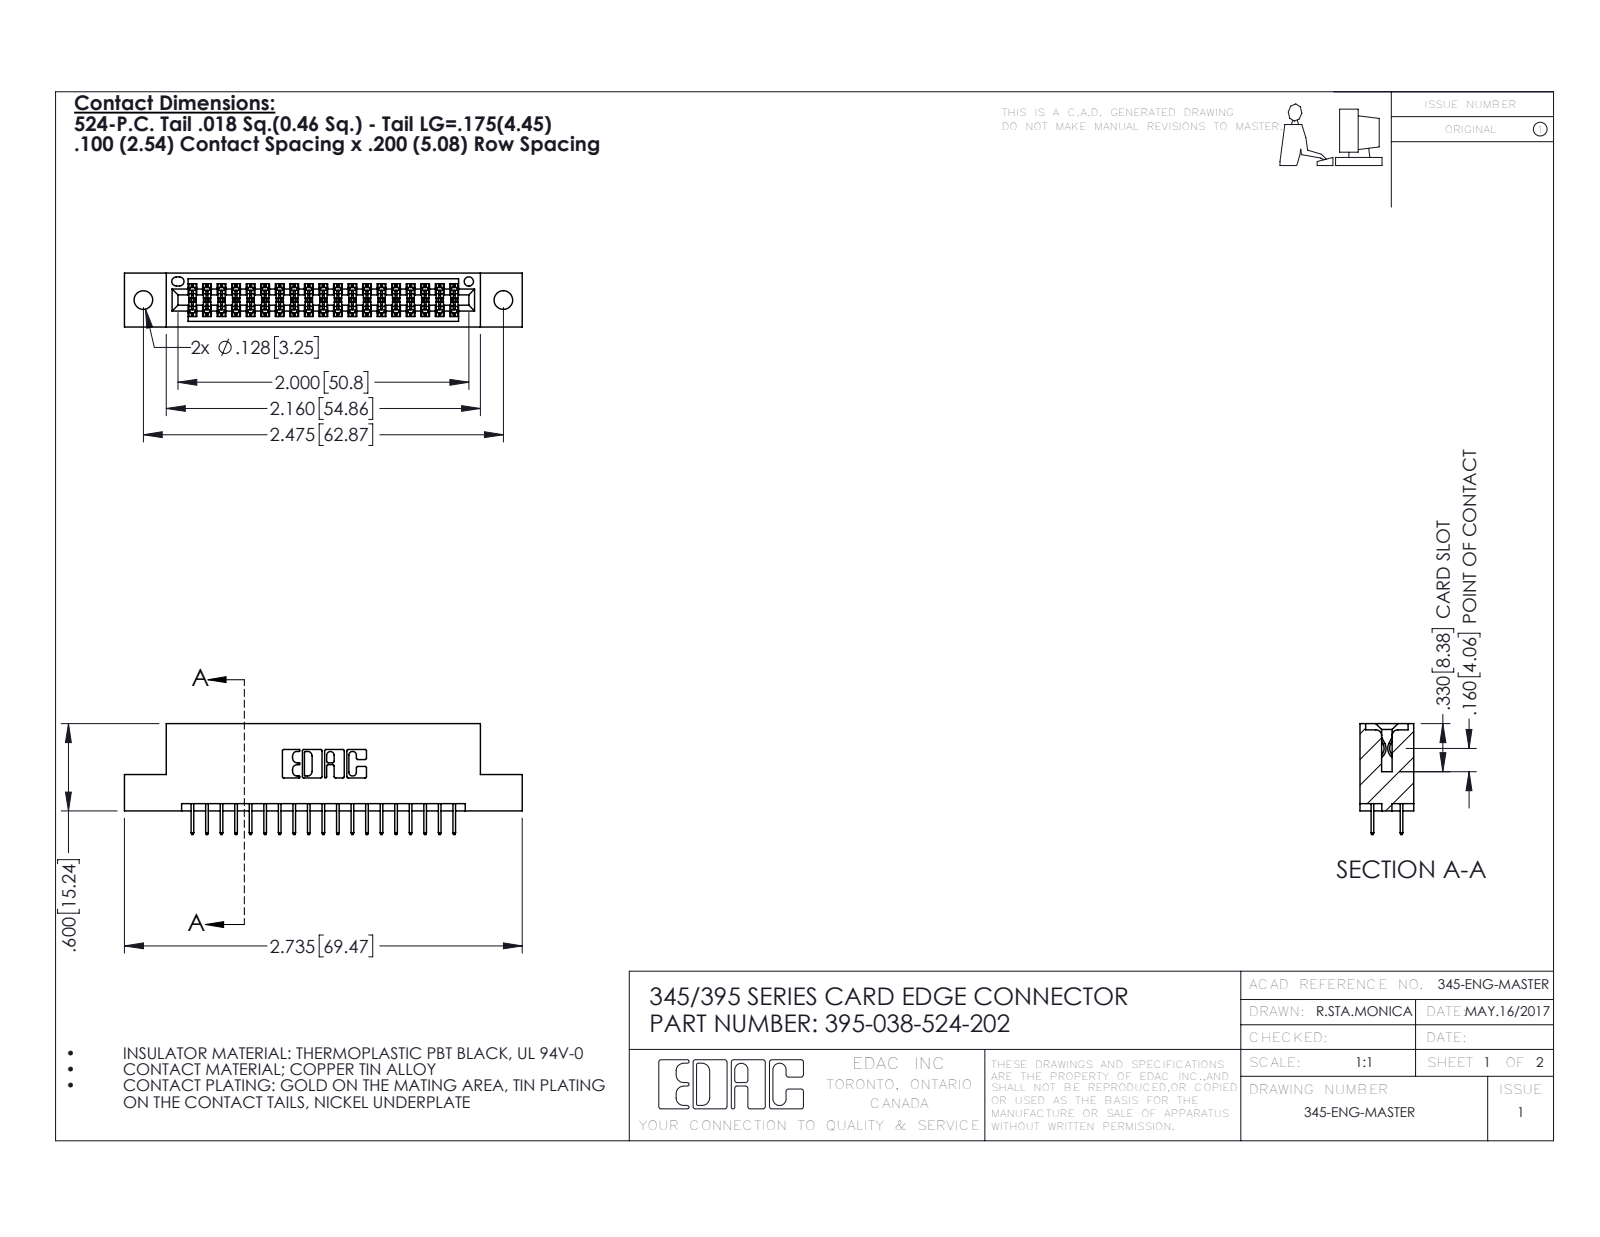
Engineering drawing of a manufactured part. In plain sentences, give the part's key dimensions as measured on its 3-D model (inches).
The part is named "345-292-001_345-293-124; 345 Part_Flush Mounting Lugs - 0.128 Dia; 395-038-524-202". Its 3-D file was written by "SolidWorks 2016 (CONFIG_CONTROL_DESIGN)". It is 39 solids with 2178 faces: 1562 planar, 616 cylindrical and 0 other. Overall it measures 2.735 by 0.762 by 0.37 inches. Its volume is 0.393 cubic inches and its surface area 13.41 square inches. Round holes: 2 of diameter 0.128, 1 of diameter 0.064. Partial cylindrical surfaces (rounded edges, fillets, slot ends): 57 of radius 0.006, 22 of radius 0.01, 6 of radius 0.007, 6 of radius 0.031, 3 of radius 0.026, 2 of radius 0.014, 2 of radius 0.019, 2 of radius 0.022. The main face-to-face distances are 0.298, 0.072, 0.2, 0.37, 0.098, 0.272, 0.025, 0.225, 0.072, 0.175. The hole center spacings are 0.27, 2.241, 2.475.
